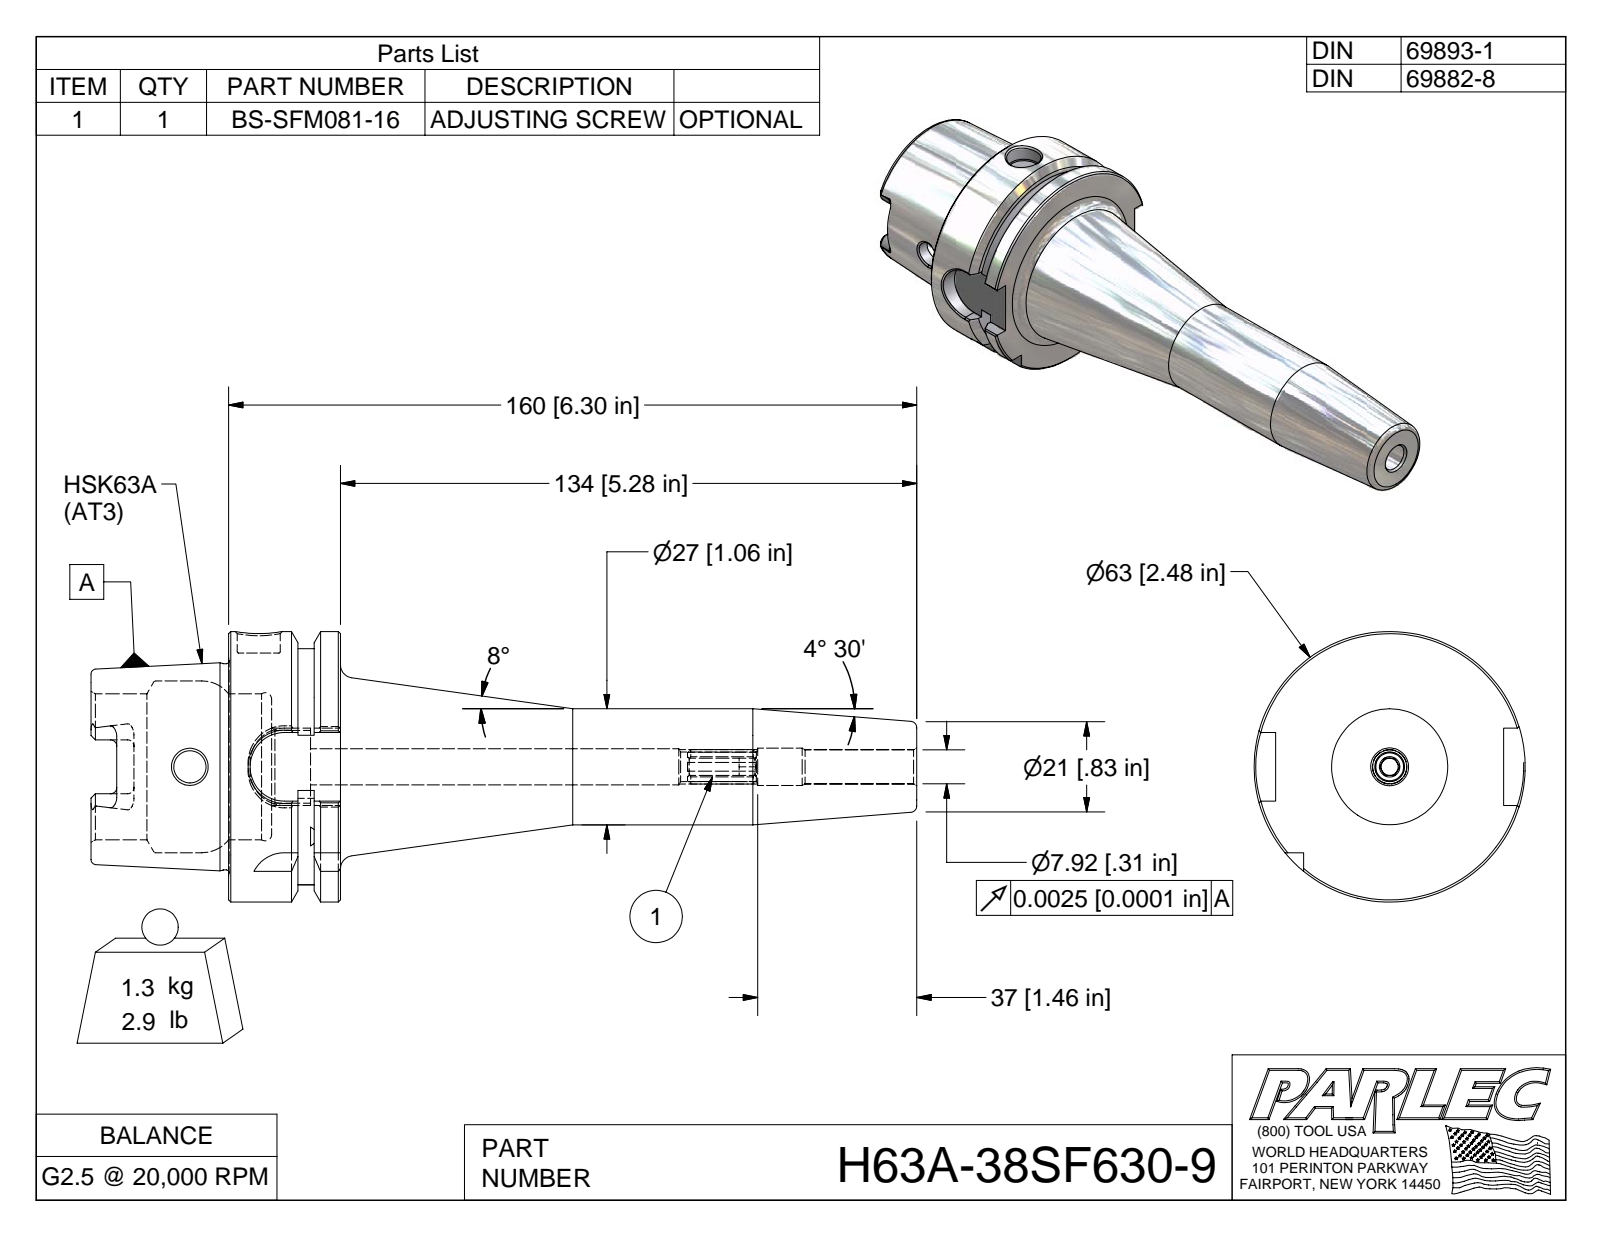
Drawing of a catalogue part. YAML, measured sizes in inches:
part_name: "H63A-38SF630-9; H63A-38SF630-9-1; BS-SFM081-16"
step_written_by: "Autodesk Inventor 2009 (AUTOMOTIVE_DESIGN)"
units: inches
bodies: {solids: 2, faces: 160, planar: 59, cylindrical: 35, other: 66}
overall_size: [7.559, 2.48, 2.48]
volume: 10.27
surface_area: 58.19
round_holes:
  - {diameter: 0.295, count: 1}
  - {diameter: 0.312, count: 1}
  - {diameter: 0.342, count: 1}
  - {diameter: 0.394, count: 1}
  - {diameter: 0.666, count: 1}
  - {diameter: 1.339, count: 1}
  - {diameter: 1.575, count: 1}
round_bosses_or_shafts:
  - {diameter: 2.48, count: 1}
  - {diameter: 1.891, count: 1}
  - {diameter: 1.063, count: 1}
partial_cylinders:
  - {radius: 0.059, count: 6}
  - {radius: 0.113, count: 4}
  - {radius: 0.315, count: 4}
  - {radius: 0.157, count: 1}
  - {radius: 1.083, count: 1}
face_to_face_distances: [1.024, 0.241, 0.389, 0.394, 0.63, 1.26, 1.654, 2.283, 1.894, 0.635]
